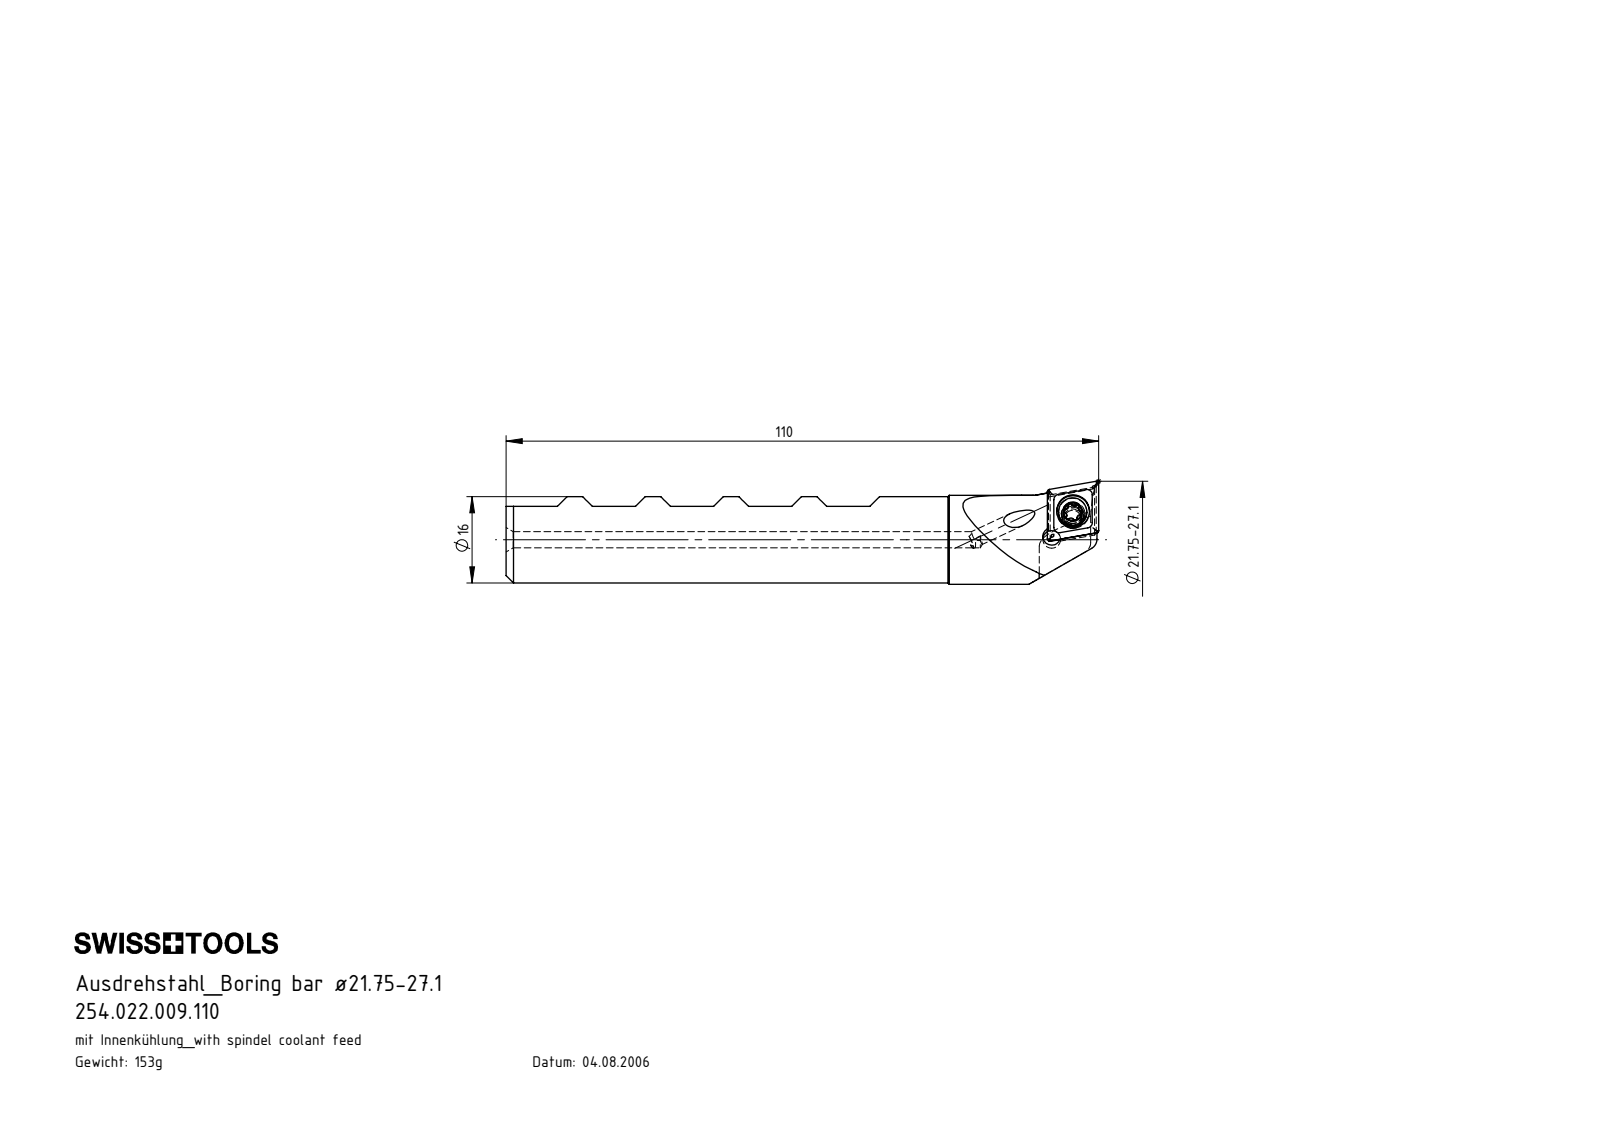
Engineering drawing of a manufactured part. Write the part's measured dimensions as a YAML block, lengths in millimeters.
part_name: "WCB-ER2.001.009_A; CCMT09T304; 254.022.009.110; B22-WCB.K11.110_B"
step_written_by: "SolidWorks 2017 (CONFIG_CONTROL_DESIGN)"
units: millimeters
bodies: {solids: 3, faces: 147, planar: 45, cylindrical: 41, other: 61}
overall_size: [110, 19.12, 17.34]
volume: 19450
surface_area: 7133
round_holes:
  - {diameter: 3, count: 2}
  - {diameter: 3.3, count: 2}
  - {diameter: 4.4, count: 1}
  - {diameter: 6.1, count: 1}
round_bosses_or_shafts:
  - {diameter: 16.5, count: 1}
  - {diameter: 16, count: 1}
  - {diameter: 5.25, count: 1}
  - {diameter: 4, count: 1}
partial_cylinders:
  - {radius: 0.34, count: 6}
  - {radius: 0.59, count: 6}
  - {radius: 2, count: 1}
  - {radius: 8.4, count: 1}
  - {radius: 12, count: 1}
face_to_face_distances: [10.25, 20.5, 30.76, 20.51, 5.94, 9.71, 3.77, 9.91, 3.97, 30.75]
hole_center_spacings: [6.07, 6.19]
